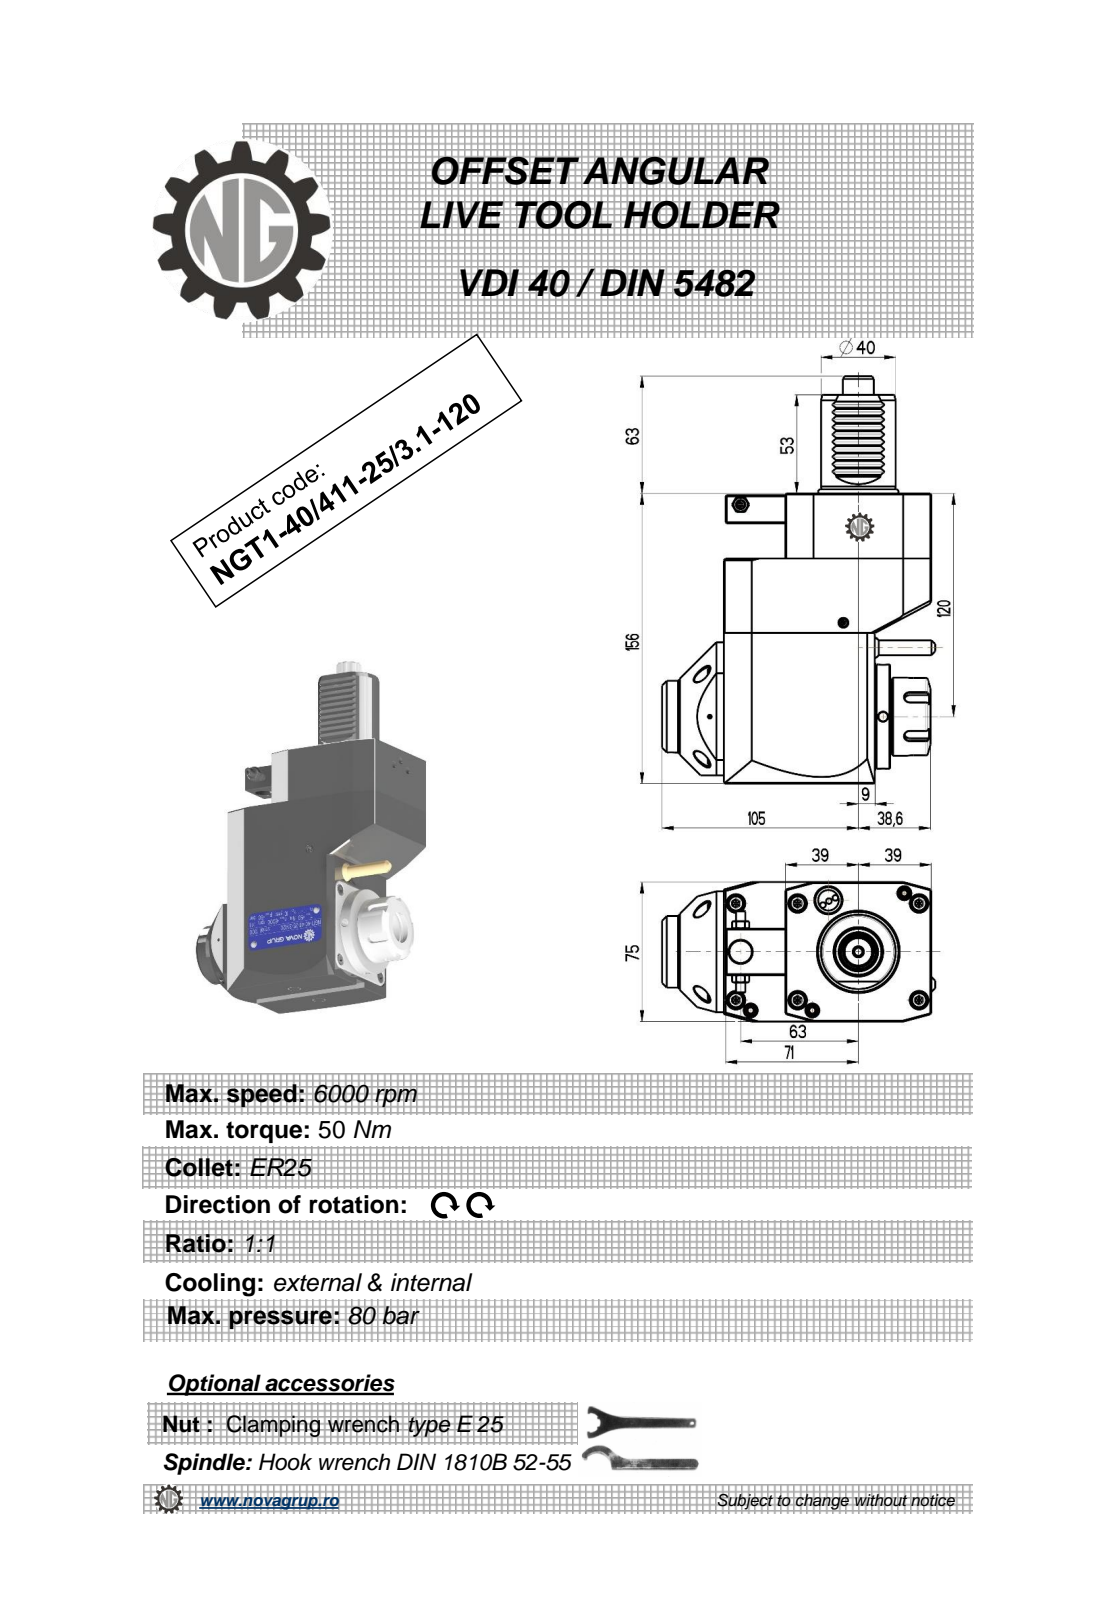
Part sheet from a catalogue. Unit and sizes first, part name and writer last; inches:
Units: inches
Overall size (bounding box): 8.622 × 5.754 × 2.953
Round holes (diameter × count): ⌀0.197 ×3, ⌀0.165 ×2, ⌀0.118 ×1, ⌀0.374 ×1, ⌀0.472 ×1, ⌀0.799 ×1
Round bosses / shafts (diameter × count): ⌀2.205 ×1, ⌀1.693 ×1, ⌀1.654 ×1, ⌀1.575 ×1, ⌀1.516 ×1, ⌀1.299 ×1, ⌀0.441 ×1, ⌀0.353 ×1
Partial cylindrical surfaces — rounded edges, fillets, slot ends (radius × count): R0.119 ×18, R0.01 ×12, R0.012 ×10, R0.009 ×6, R0.118 ×5, R0.02 ×1, R0.266 ×1, R0.325 ×1
Main face-to-face distances: 2.953, 6.142, 4.37, 1.299, 1.378, 4.764, 3.189, 1.181, 1.89, 3.071
Hole centre spacings: 0.522, 1.611, 2.48, 3.002, 3.051, 4.429, 5.4
Volume: 72.92 in³ · Surface area: 137.5 in²
Bodies: 1 solid, 483 faces (197 planar, 122 cylindrical, 164 other)
Part name (STEP PRODUCT): NGT1_40_411_25_3_1_120
STEP written by: PRO/ENGINEER BY PARAMETRIC TECHNOLOGY CORPORATION, 2010280 (CONFIG_CONTROL_DESIGN)
